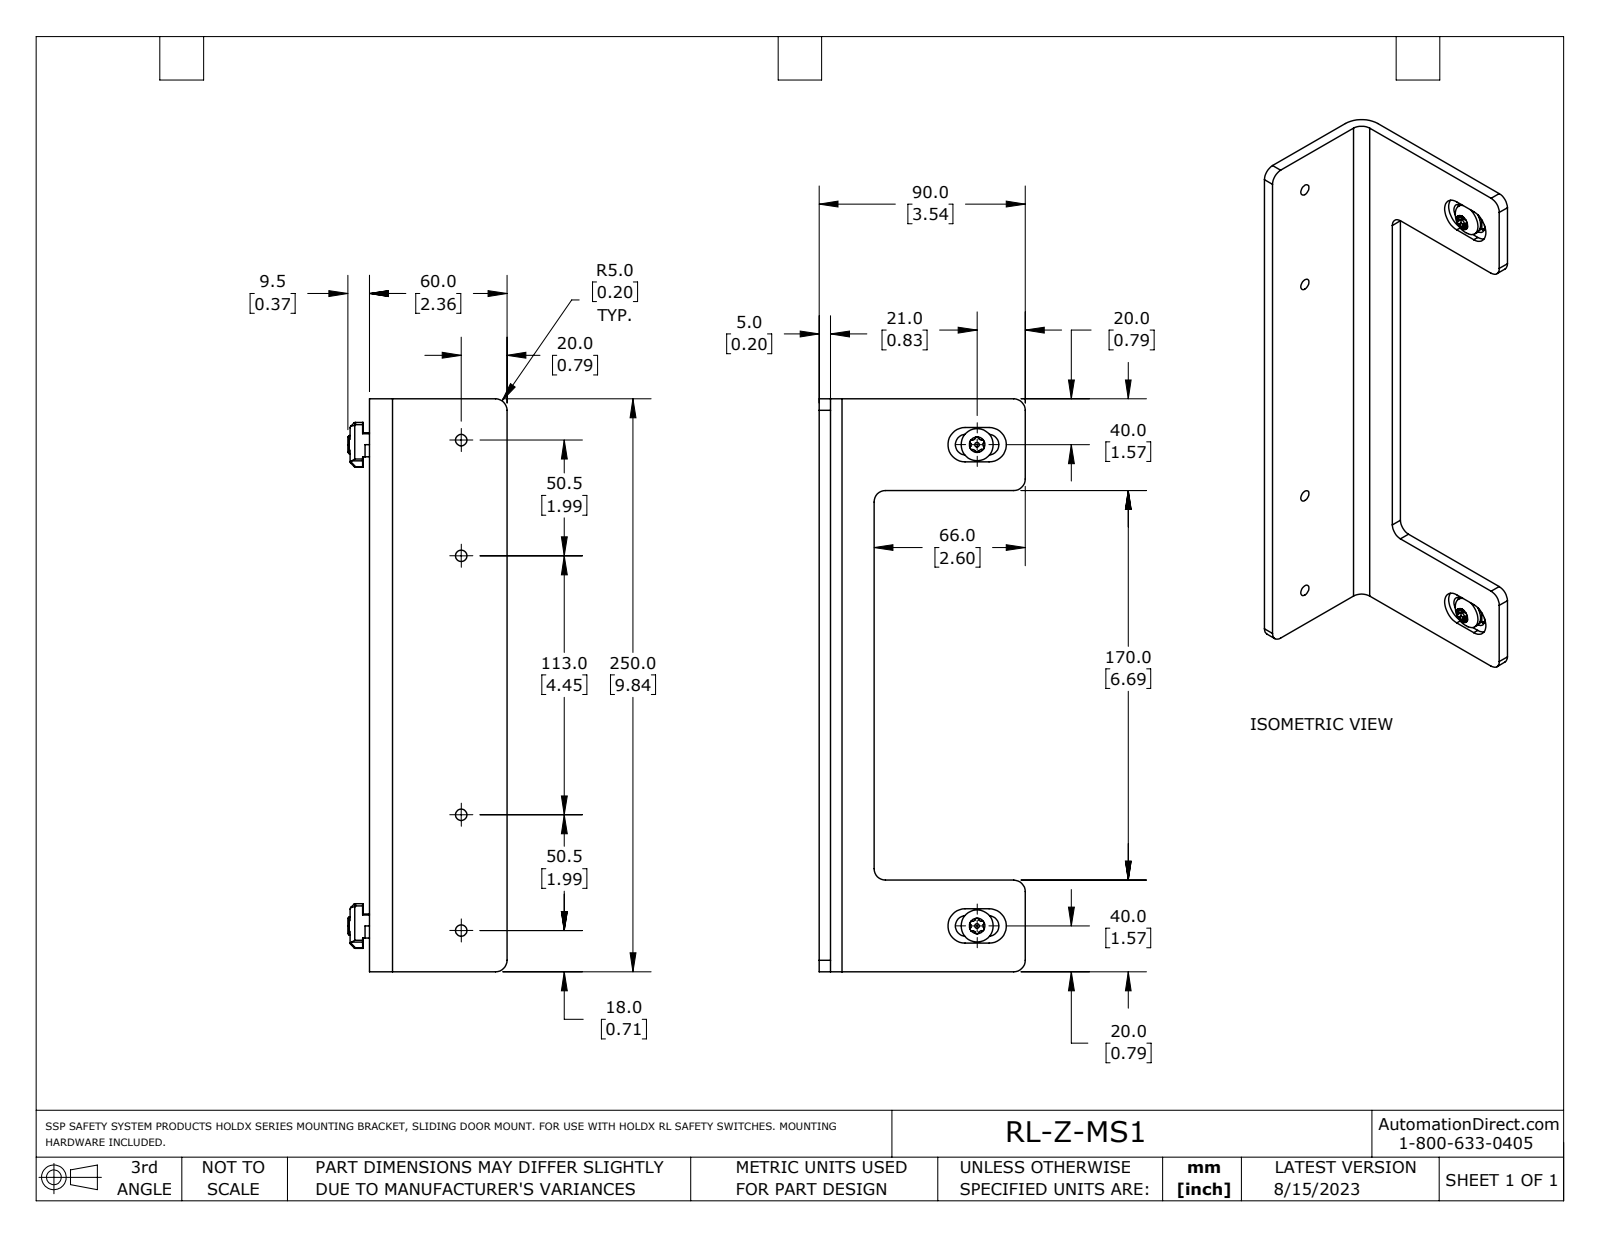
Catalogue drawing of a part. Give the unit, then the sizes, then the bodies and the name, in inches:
Units: inches
Overall size (bounding box): 9.843 × 3.543 × 2.736
Round holes (diameter × count): ⌀0.197 ×6, ⌀0.266 ×2
Round bosses / shafts (diameter × count): ⌀0.551 ×2, ⌀0.315 ×2, ⌀0.079 ×2
Partial cylindrical surfaces — rounded edges, fillets, slot ends (radius × count): R0.011 ×48, R0.039 ×30, R0.056 ×24, R0.197 ×9, R0.02 ×4, R0.177 ×4, R0.295 ×4, R0.079 ×2
Main face-to-face distances: 0.197, 2.362, 2.165, 0.098, 0.945, 0.748, 8.268, 9.843, 2.264, 1.575
Hole centre spacings: 1.988, 6.437, 4.449, 8.268, 8.425
Volume: 7.478 in³ · Surface area: 87.24 in²
Bodies: 5 solids, 280 faces (116 planar, 148 cylindrical, 16 other)
Part name (STEP PRODUCT): RL-Z-MS1_REV1
STEP written by: SolidWorks 2021 (AUTOMOTIVE_DESIGN)
